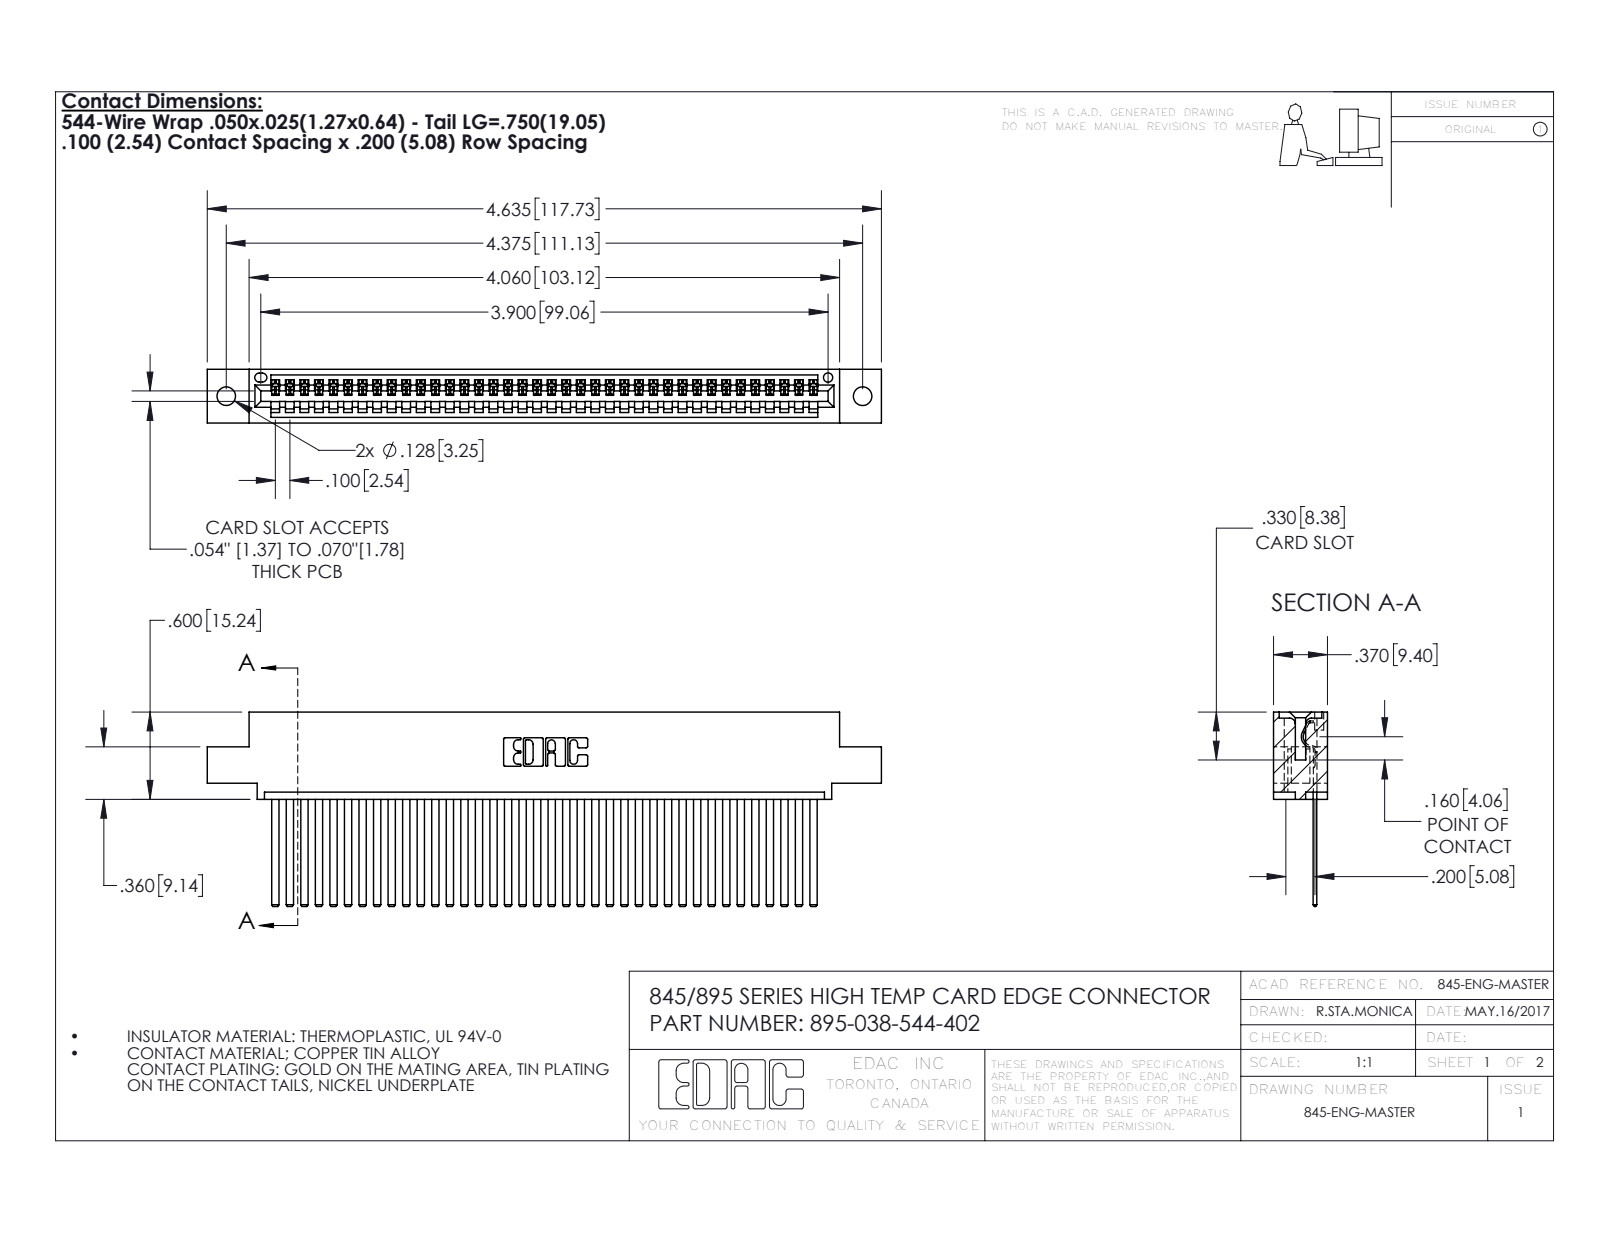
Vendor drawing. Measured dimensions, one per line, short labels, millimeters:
name: 345 Part_0.110 Offset - 0.128 Dia; 345-292-001_345-293-144; 395-038-544-402
written by: SolidWorks 2016 (CONFIG_CONTROL_DESIGN)
unit: mm
bodies: 39 solids, 2106 faces (1452 planar, 654 cylindrical, 0 other)
size: 117.7 × 34 × 9.4
volume: 11 500 mm³; area: 16 330 mm²
holes: 2× ⌀3.3, 1× ⌀1.6
rounds: 76× R0.2, 22× R0.3, 6× R0.2, 6× R0.8, 3× R0.7, 2× R0.8, 2× R1, 1× R0.4
face distances: 1.8, 7.6, 0.6, 2.5, 6.9, 9.4, 5.1, 5.7, 3.8, 1.8
hole spacings: 6.9, 105.1, 111.1
